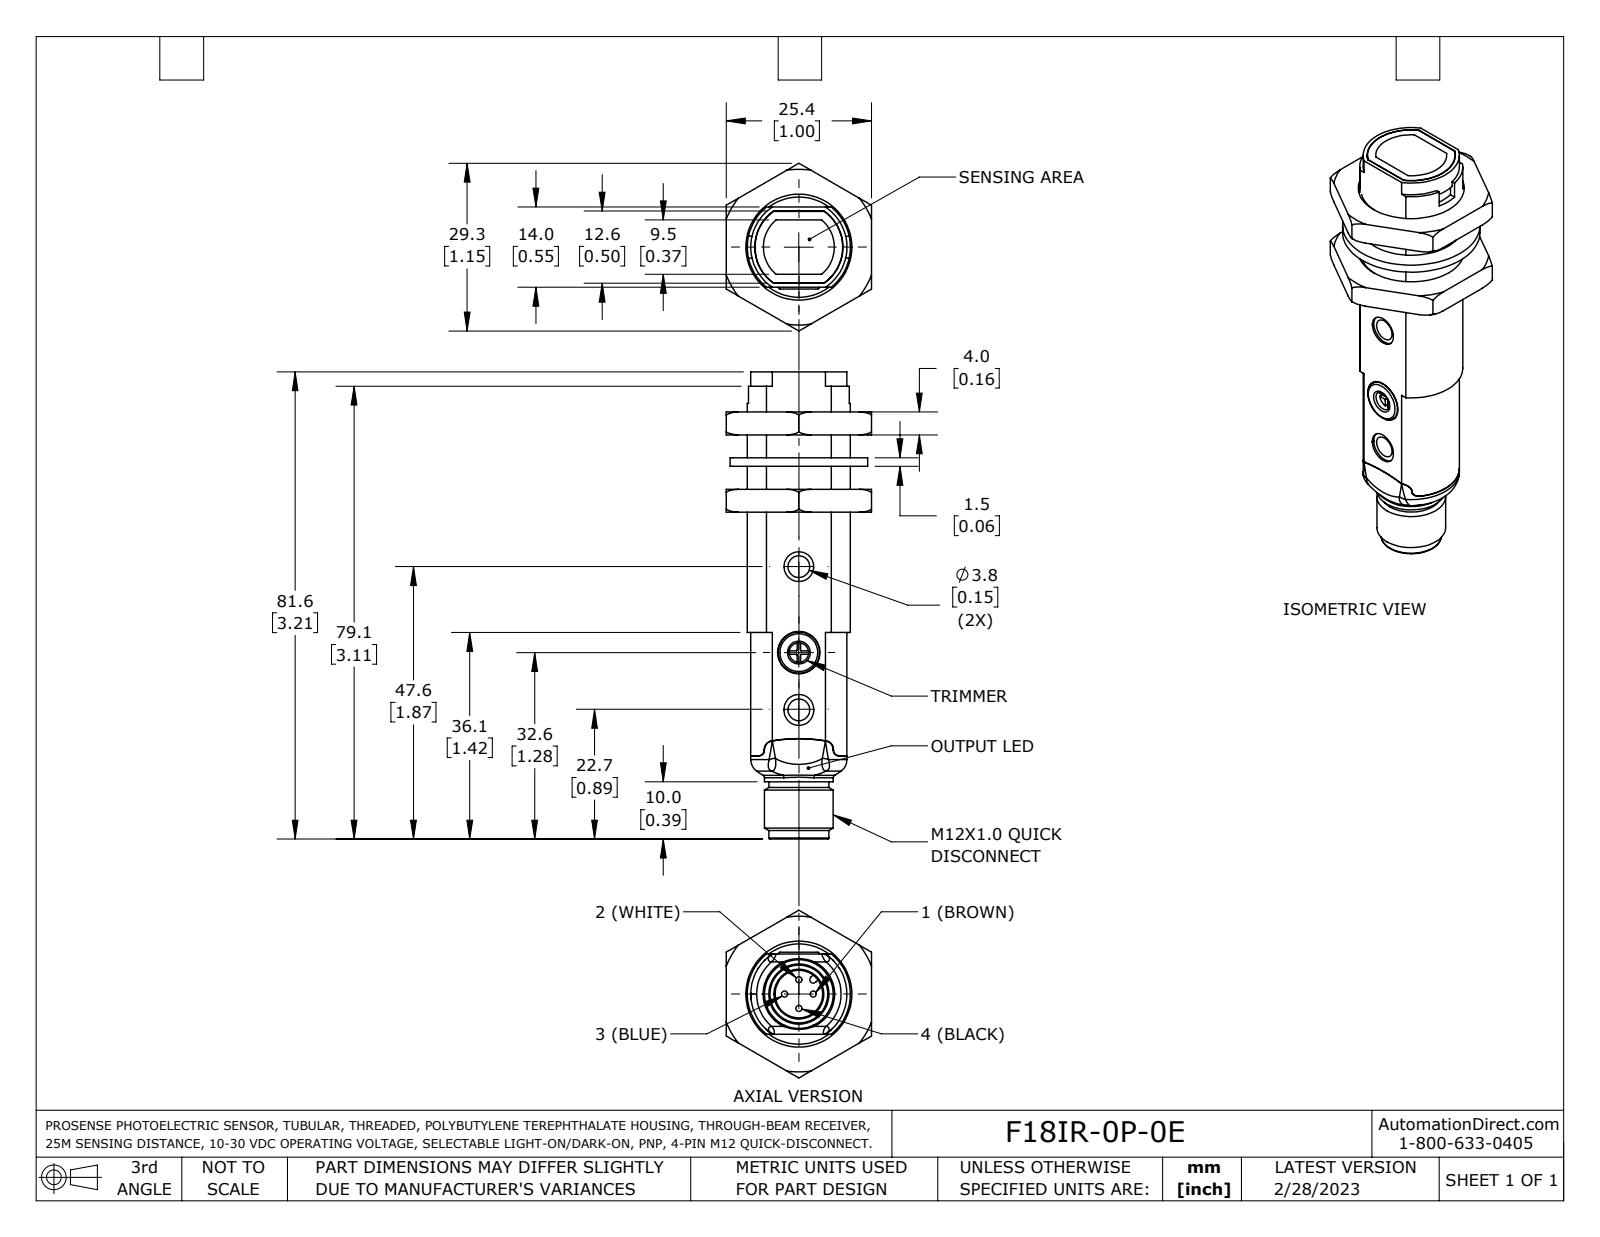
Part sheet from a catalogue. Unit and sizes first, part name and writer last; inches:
Units: inches
Overall size (bounding box): 3.211 × 1.153 × 0.998
Round holes (diameter × count): ⌀0.15 ×2, ⌀0.134 ×1, ⌀0.205 ×1, ⌀0.291 ×1, ⌀0.689 ×1
Round bosses / shafts (diameter × count): ⌀0.042 ×4, ⌀0.945 ×1, ⌀0.709 ×1, ⌀0.472 ×1, ⌀0.413 ×1, ⌀0.283 ×1
Partial cylindrical surfaces — rounded edges, fillets, slot ends (radius × count): R0.039 ×4, R0.059 ×4, R0.102 ×2, R1.102 ×2, R0.02 ×1, R0.024 ×1, R0.301 ×1, R0.303 ×1
Main face-to-face distances: 0.157, 0.374, 0.551, 0.531, 0.217, 0.315, 0.998, 0.689, 0.433, 0.059
Hole centre spacings: 0.394, 0.591, 0.984
Volume: 1.116 in³ · Surface area: 13 in²
Bodies: 4 solids, 197 faces (86 planar, 54 cylindrical, 57 other)
Part name (STEP PRODUCT): F18IR-0P-0E
STEP written by: SolidWorks 2021 (AUTOMOTIVE_DESIGN)
